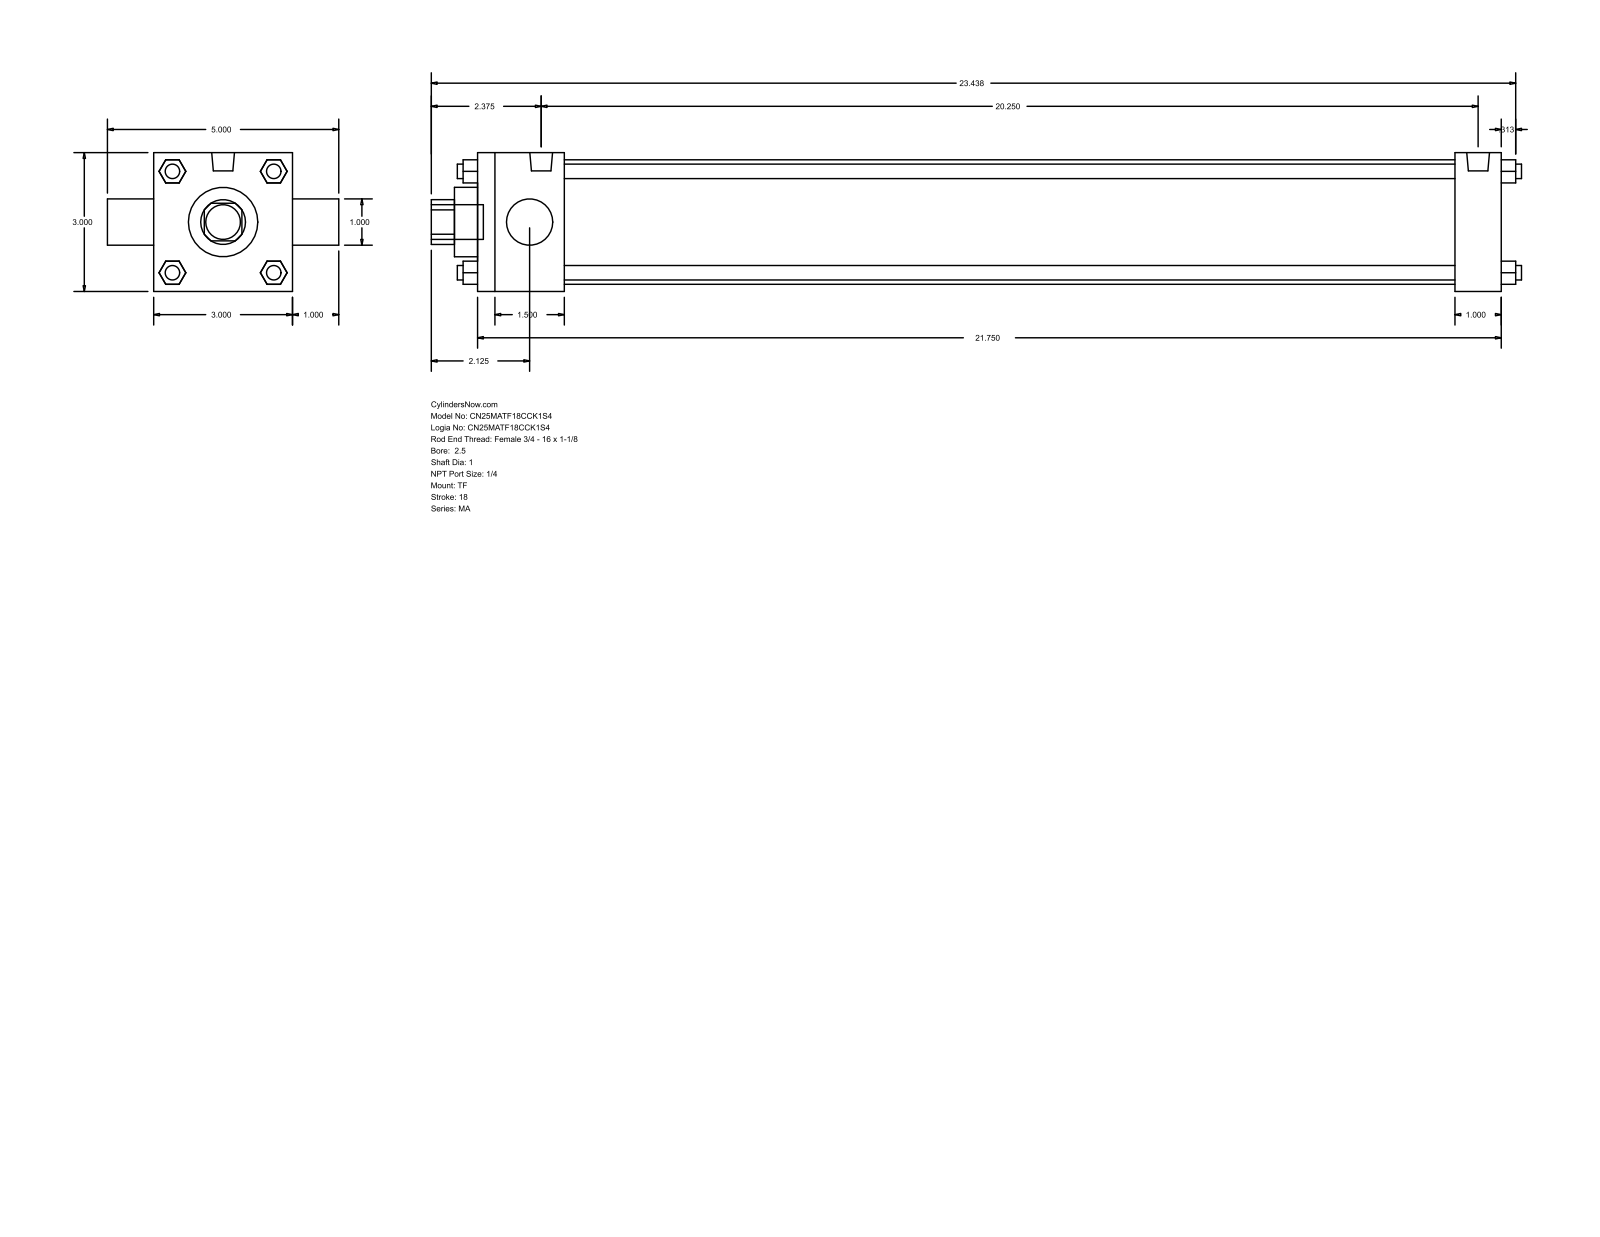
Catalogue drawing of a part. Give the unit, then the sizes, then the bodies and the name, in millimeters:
Units: millimetres
Overall size (bounding box): 598.49 × 127 × 76.2
Round holes (diameter × count): ⌀25.4 ×2, ⌀38.1 ×1, ⌀68.33 ×1
Round bosses / shafts (diameter × count): ⌀7.94 ×7, ⌀12.49 ×2, ⌀19.05 ×1
Partial cylindrical surfaces — rounded edges, fillets, slot ends (radius × count): R12.29 ×1
Main face-to-face distances: 76.2, 561.98, 25.4, 12.7, 47.63, 536.58, 488.95, 514.35, 101.6, 27.81
Bodies: 0 solids, 120 faces (92 planar, 28 cylindrical, 0 other)
Part name (STEP PRODUCT): MA_TF__0250_1
STEP written by: GSSL Pune (CONFIG_CONTROL_DESIGN)
